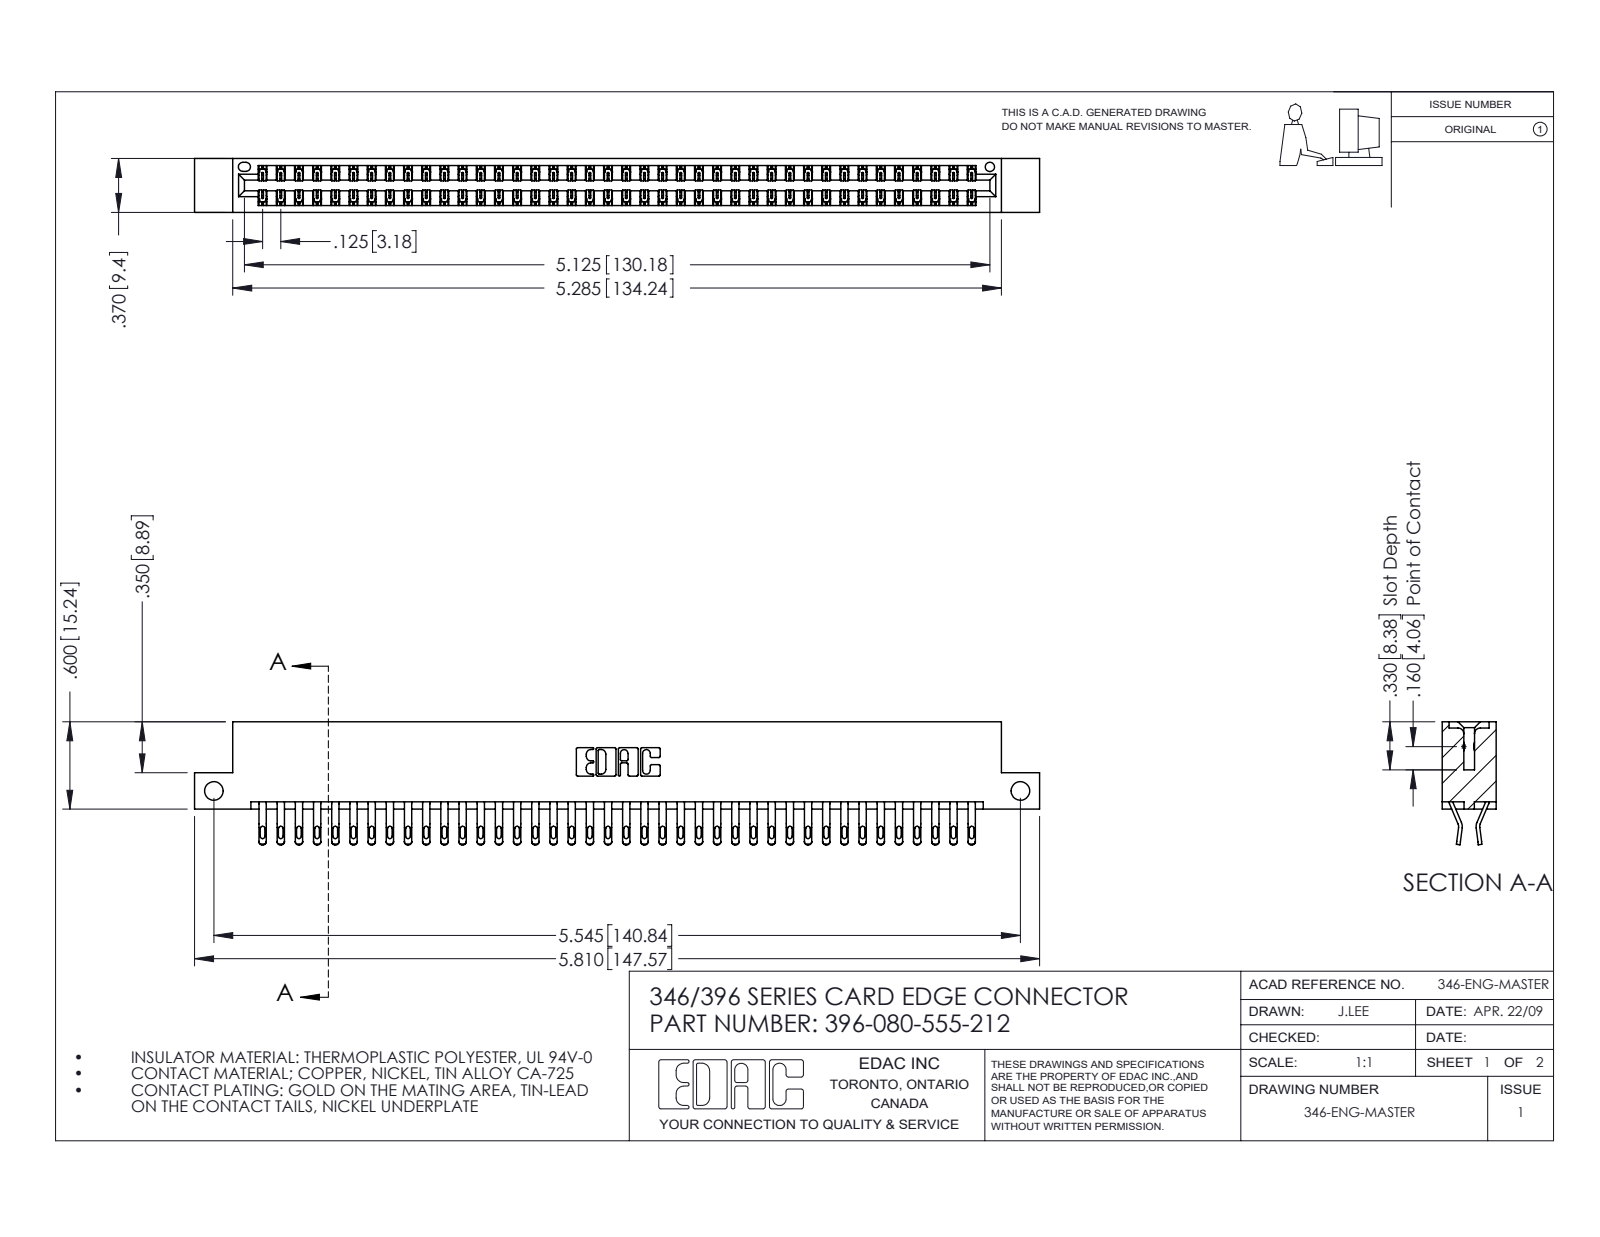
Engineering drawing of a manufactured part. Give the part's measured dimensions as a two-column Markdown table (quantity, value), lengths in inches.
| quantity | value |
| --- | --- |
| part name | 346 Part_Flush Mounting Lugs - Side Mount; 396-080-555-212; 345-292-001_555 Tail |
| STEP written by | SolidWorks 2016 (CONFIG_CONTROL_DESIGN) |
| units | inches |
| bodies | 81 solids, 4762 faces (2716 planar, 2046 cylindrical, 0 other) |
| overall size | 5.81 × 0.845 × 0.37 |
| volume | 0.886 in³ |
| surface area | 31.96 in² |
| round holes (diameter × count) | 0.128 × 2, 0.064 × 1 |
| partial cylindrical surfaces (radius × count) | 0.016 × 160, 0.02 × 160, 0.006 × 120, 0.01 × 22, 0.007 × 6, 0.031 × 6, 0.026 × 3, 0.01 × 2 |
| main face-to-face distances | 0.048, 0.322, 0.37, 0.25, 0.025, 0.072, 0.298, 0.275, 0.148, 0.222 |
| hole center spacings | 5.545 |
